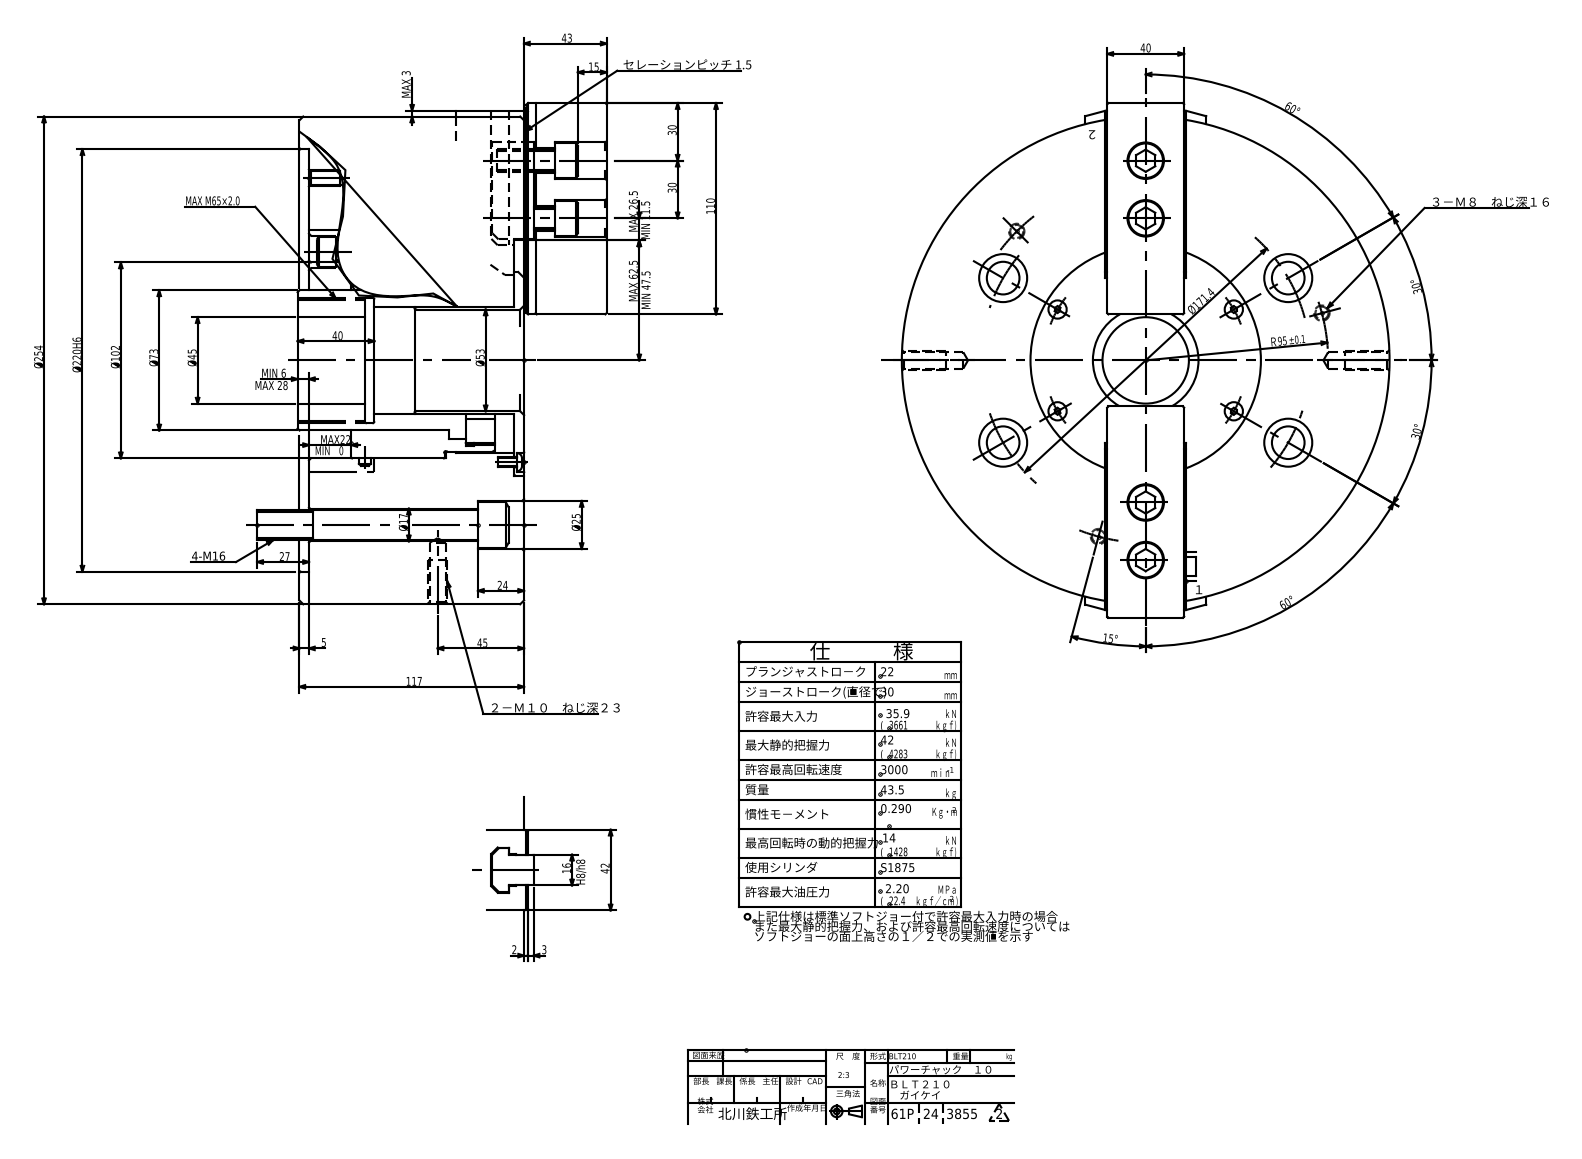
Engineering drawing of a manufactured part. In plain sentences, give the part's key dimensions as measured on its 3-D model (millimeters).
The part is named "BLT210-Solid". Its 3-D file was written by "ST-DEVELOPER v16.7 (AUTOMOTIVE_DESIGN)". It is 1 solid with 2419 faces: 1728 planar, 537 cylindrical and 154 other. Overall it measures 254 by 254 by 182.2 millimeters. Its volume is 5 639 000 cubic millimeters and its surface area 410 266 square millimeters. Round holes: 4 of diameter 4.2, 4 of diameter 5.5, 4 of diameter 10, 4 of diameter 10.3, 4 of diameter 13, 4 of diameter 17, 4 of diameter 19, 4 of diameter 25, 3 of diameter 6.8, 1 of diameter 8.5, 1 of diameter 45, 1 of diameter 53. Round bosses or shafts: 4 of diameter 24, 4 of diameter 18, 4 of diameter 15.68, 4 of diameter 11.7, 4 of diameter 9.5, 4 of diameter 4.83, 1 of diameter 254, 1 of diameter 95. Partial cylindrical surfaces (rounded edges, fillets, slot ends): 92 of radius 0.1, 4 of radius 0.8, 4 of radius 11.5, 2 of radius 5, 2 of radius 8.5, 1 of radius 0.51, 1 of radius 2.19, 1 of radius 4.08. The main face-to-face distances are 112, 5, 117, 40, 160.2, 155.2, 43.2, 12, 16, 17. The hole center spacings are 53, 85.72, 32.72, 60.72, 74.93, 77.84, 83.5, 91.44.
